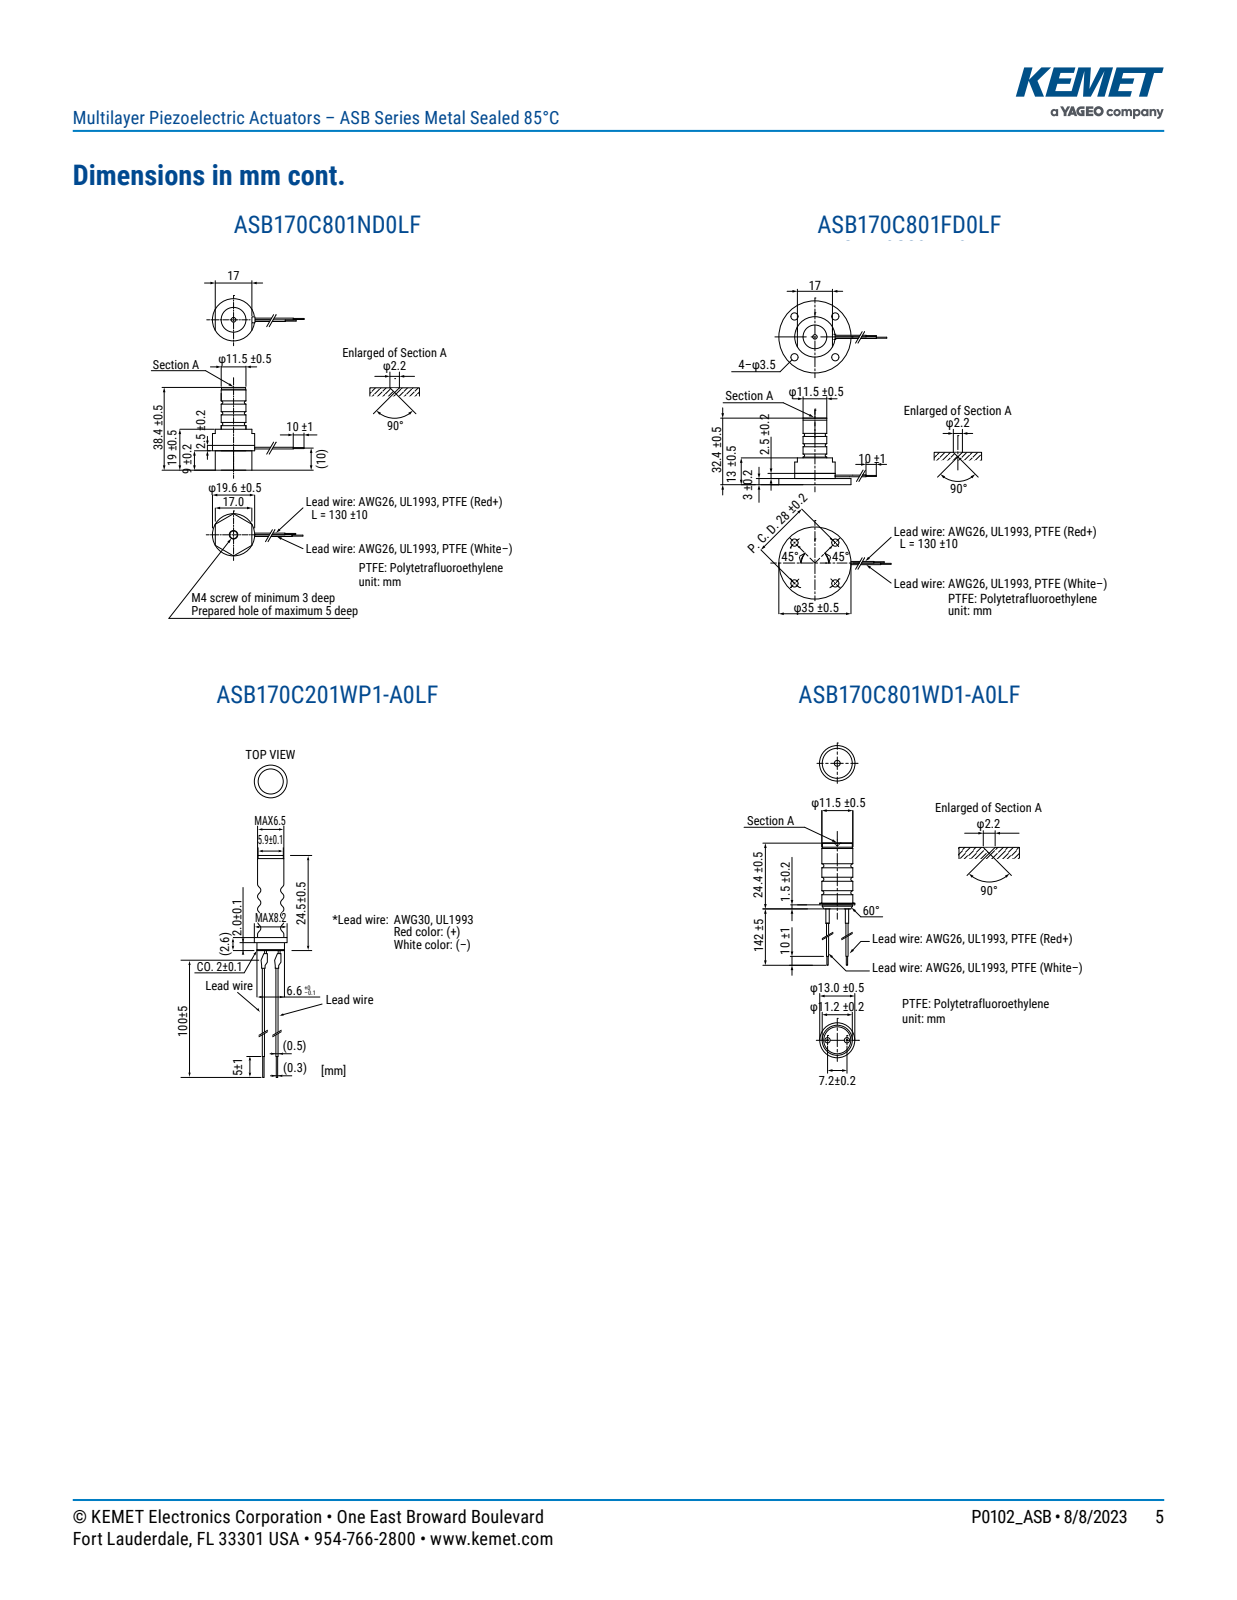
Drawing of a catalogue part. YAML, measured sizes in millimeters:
part_name: "AL_TPFE_D20.1L38.9"
step_written_by: "SolidWorks 2014 (AUTOMOTIVE_DESIGN)"
units: millimeters
bodies: {solids: 2, faces: 98, planar: 70, cylindrical: 12, other: 16}
overall_size: [44.91, 20.1, 20.1]
volume: 8410
surface_area: 3071
round_bosses_or_shafts:
  - {diameter: 20.1, count: 1}
  - {diameter: 12, count: 1}
face_to_face_distances: [19.5, 17.24, 44.9, 25.4, 17, 9.2, 10.3, 35.7, 17.5, 8.3]
